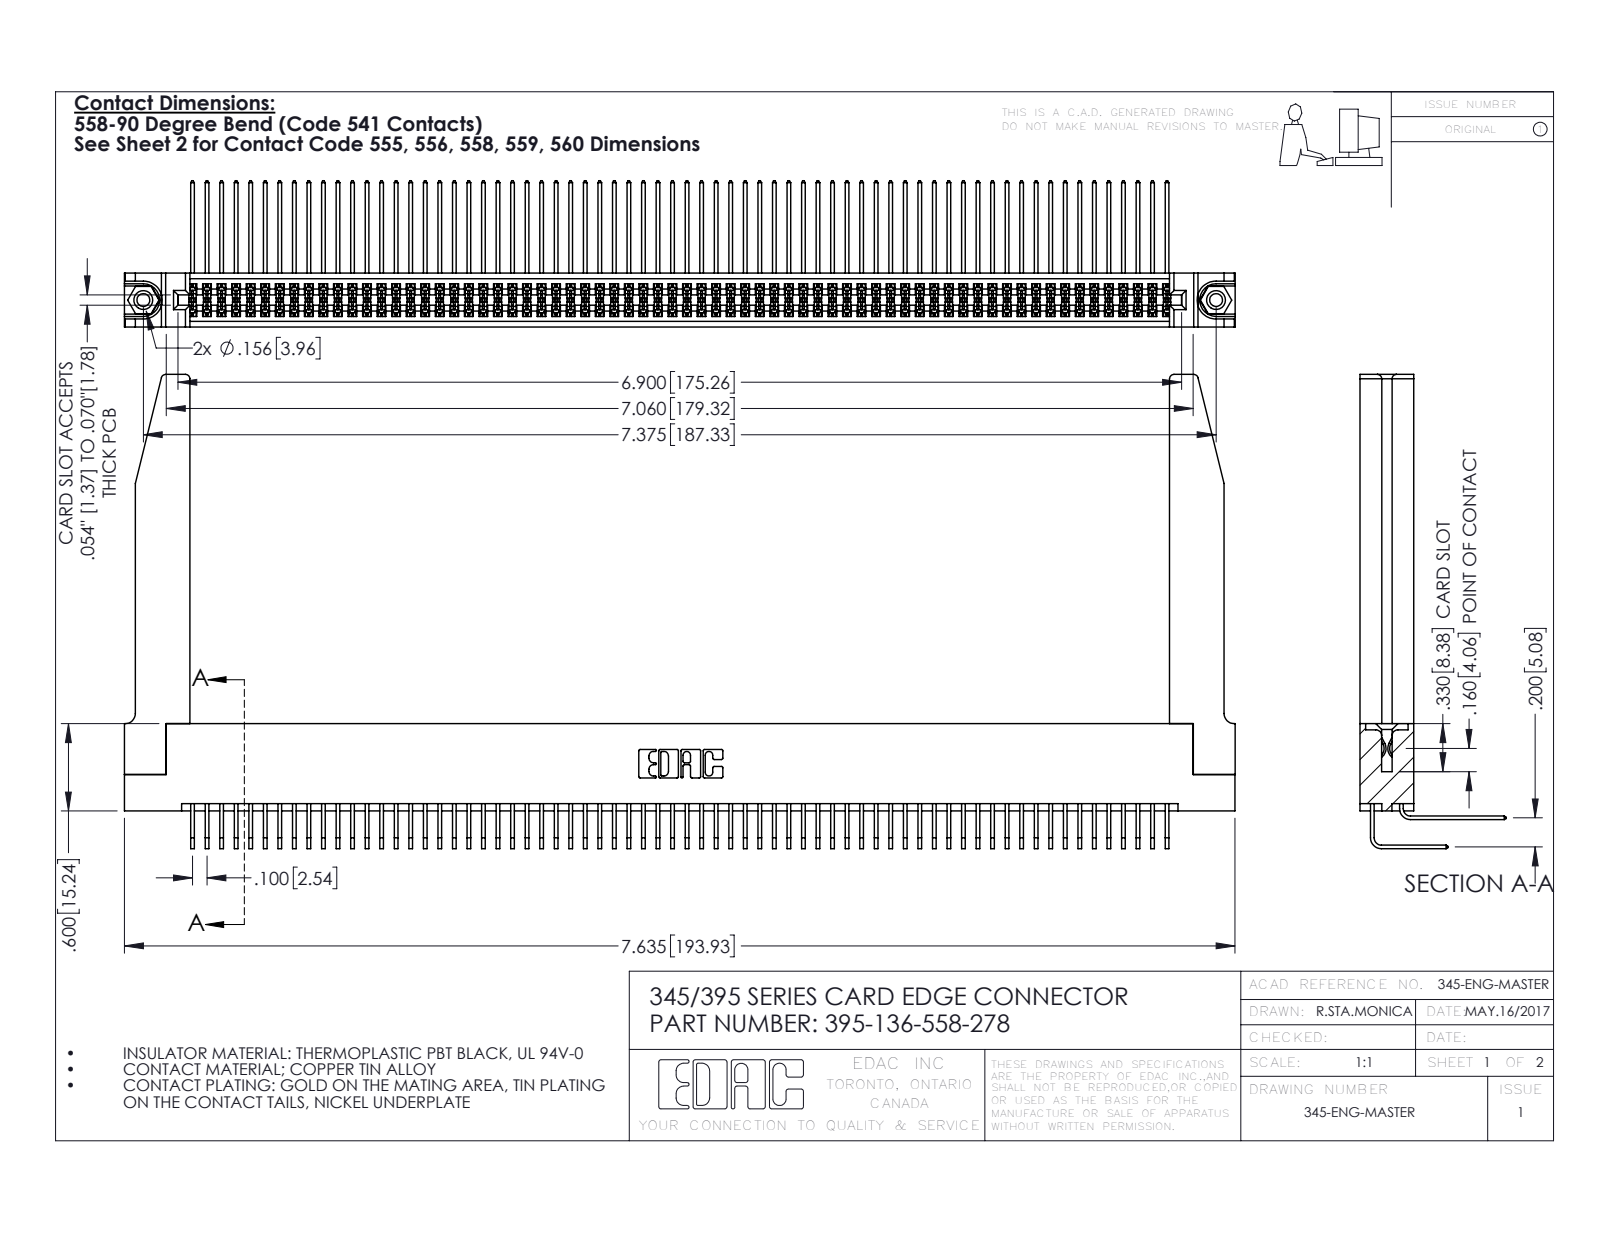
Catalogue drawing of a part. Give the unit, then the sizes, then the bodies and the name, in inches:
Units: inches
Overall size (bounding box): 7.636 × 3.259 × 1.005
Round holes (diameter × count): ⌀0.089 ×2, ⌀0.125 ×2, ⌀0.156 ×2, ⌀0.064 ×1
Round bosses / shafts (diameter × count): ⌀0.155 ×2
Partial cylindrical surfaces — rounded edges, fillets, slot ends (radius × count): R0.006 ×271, R0.01 ×22, R0.03 ×8, R0.007 ×6, R0.031 ×6, R0.026 ×3, R0.014 ×2, R0.019 ×2
Main face-to-face distances: 0.072, 0.298, 0.37, 0.2, 0.098, 0.272, 0.025, 0.225, 0.025, 0.175
Hole centre spacings: 0.27, 7.139, 7.375
Volume: 1.687 in³ · Surface area: 62.62 in²
Bodies: 141 solids, 7432 faces (4982 planar, 2398 cylindrical, 52 other)
Part name (STEP PRODUCT): 345 Part_Flush Mounting Lugs - 0.156 Dia-TH; 345-220-078_345-220-078; 345-292-001_558 Tail - 2; 395-136-558-278 (+2 more)
STEP written by: SolidWorks 2016 (CONFIG_CONTROL_DESIGN)
